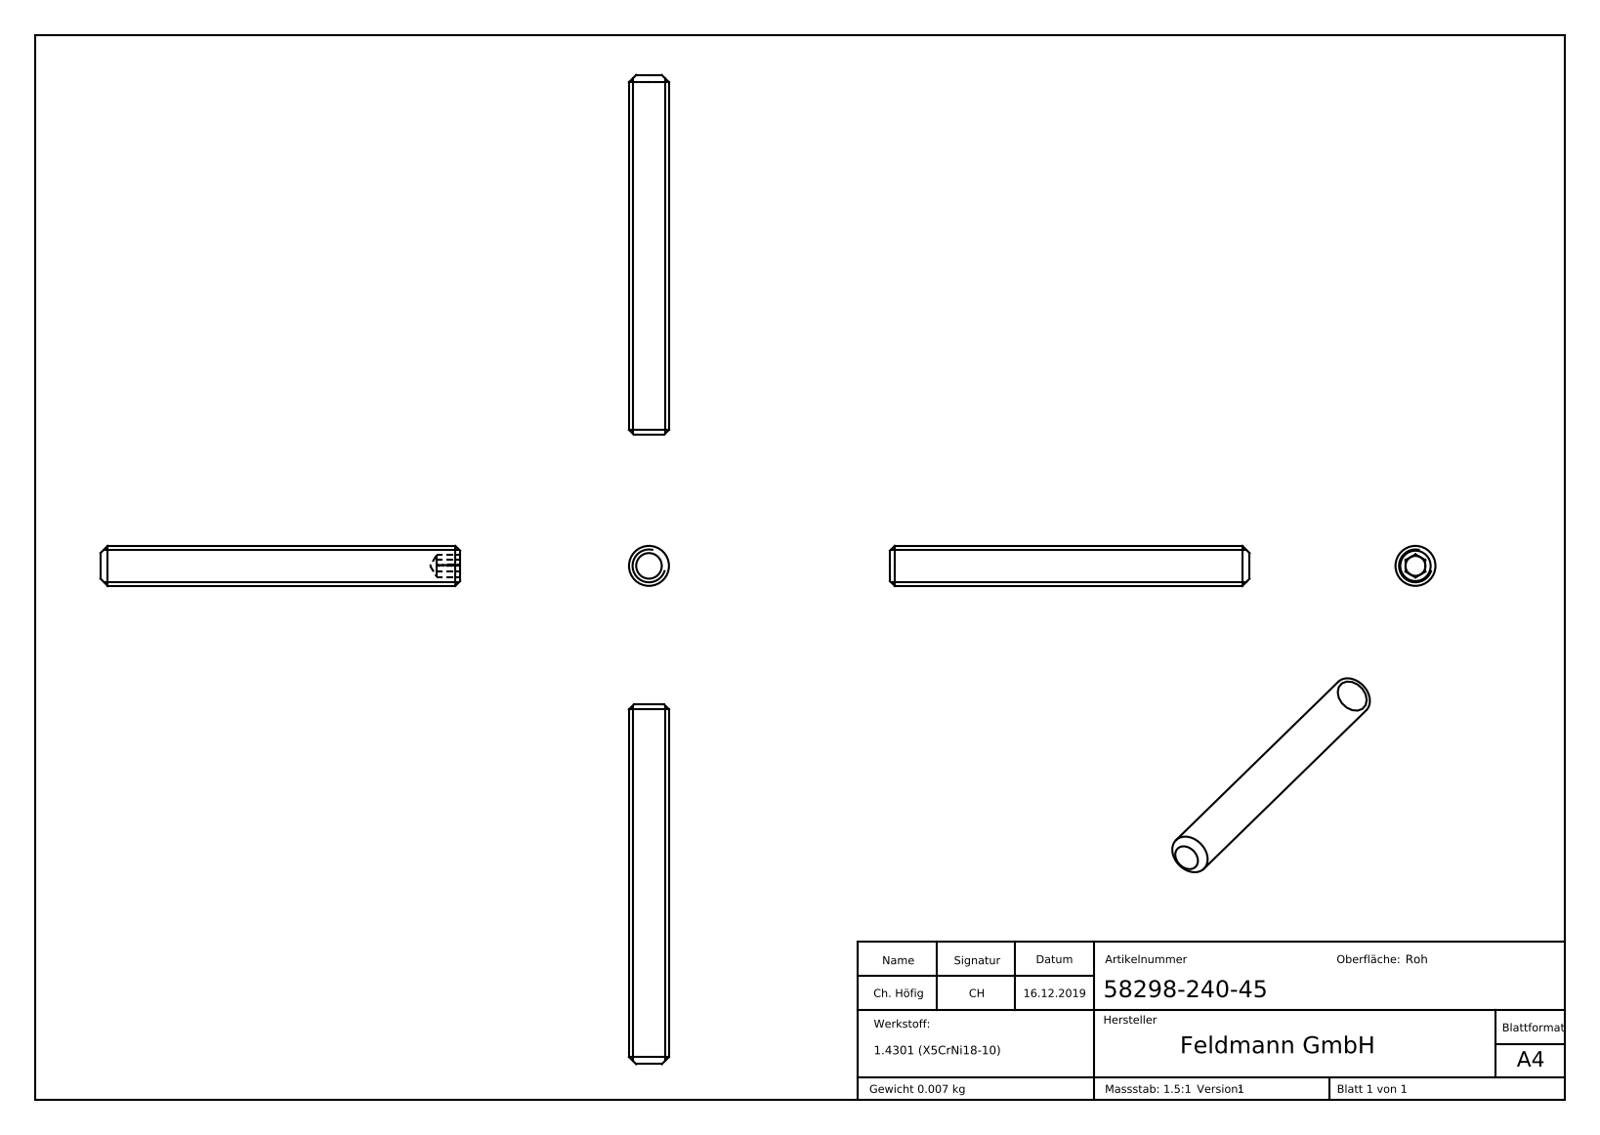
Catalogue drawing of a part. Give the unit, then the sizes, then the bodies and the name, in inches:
Units: inches
Overall size (bounding box): 2.756 × 0.197 × 0.197
Round bosses / shafts (diameter × count): ⌀0.197 ×1
Main face-to-face distances: 0.098, 1.772, 1.654, 0.118, 0.102, 0.012, 0.019, 0.021, 0.017, 0.1
Volume: 0.052 in³ · Surface area: 1.18 in²
Bodies: 1 solid, 307 faces (157 planar, 1 cylindrical, 149 other)
Part name (STEP PRODUCT): 58298-240-45
STEP written by: SolidWorks 2015 (CONFIG_CONTROL_DESIGN)
